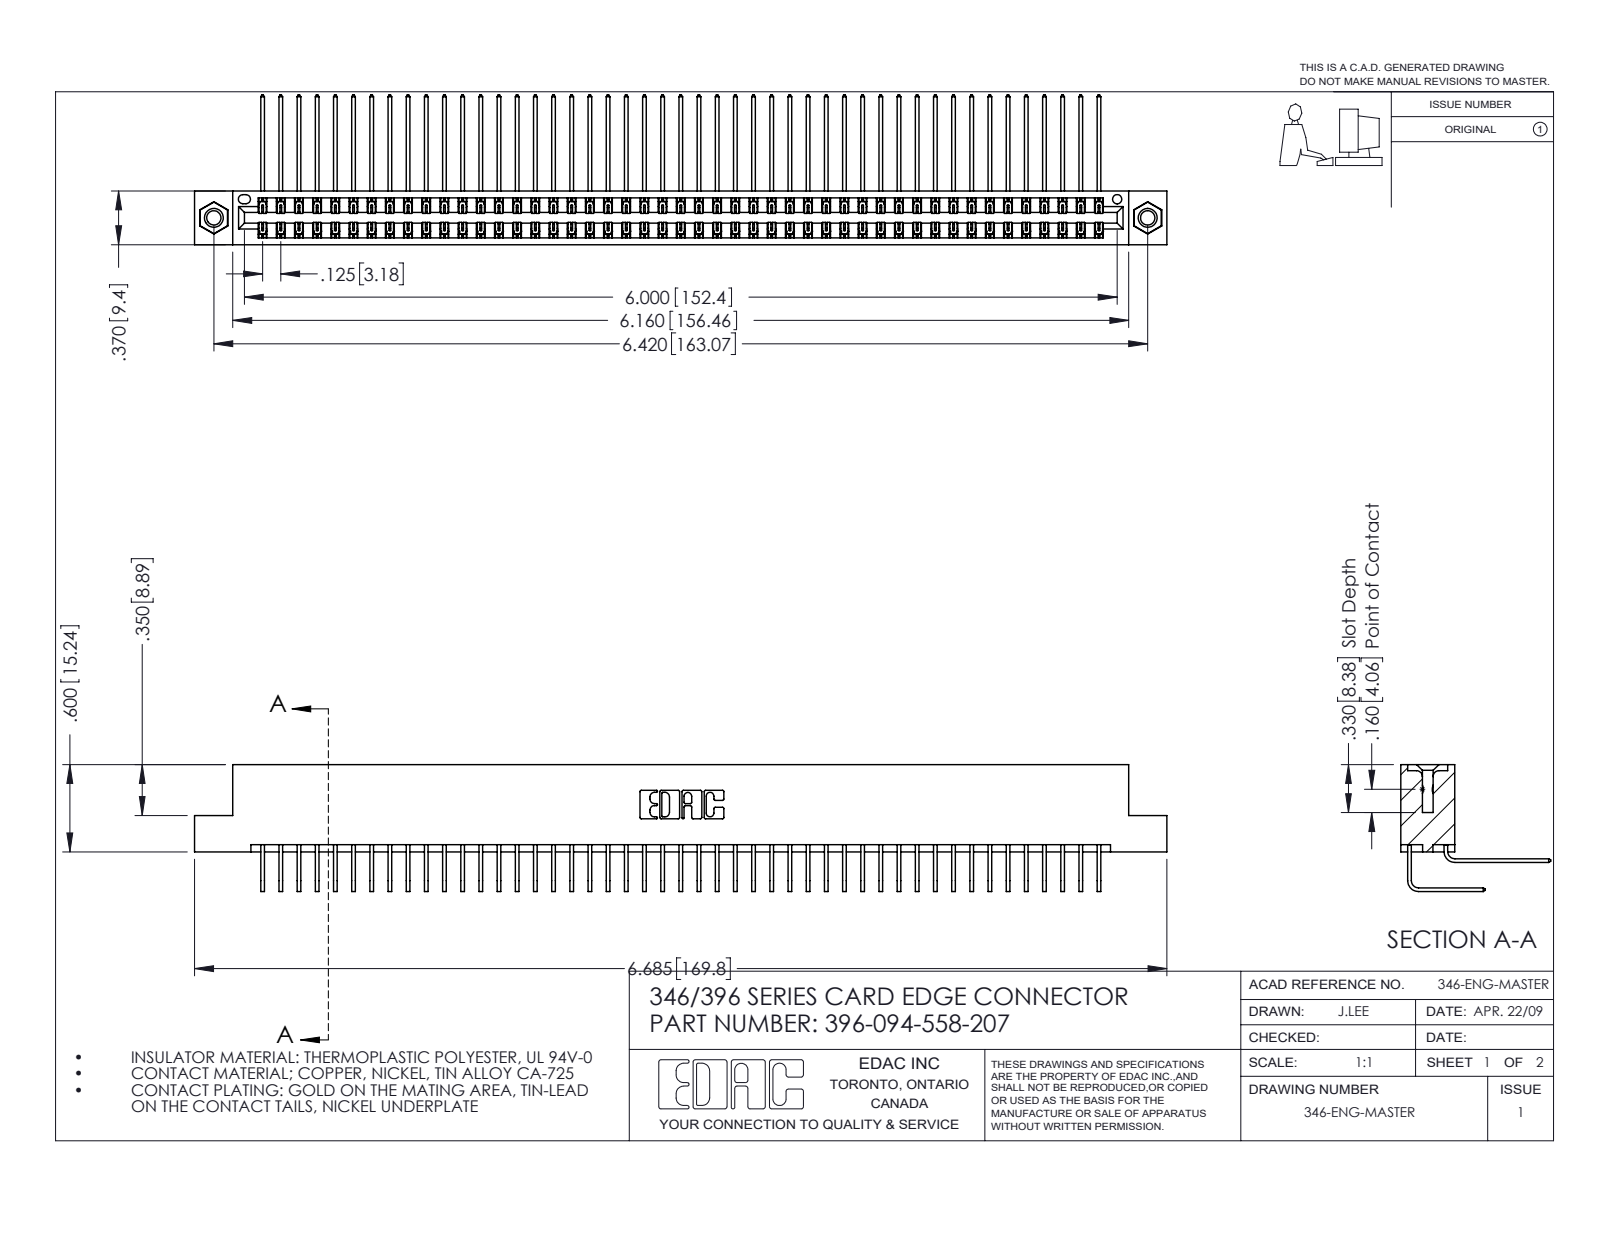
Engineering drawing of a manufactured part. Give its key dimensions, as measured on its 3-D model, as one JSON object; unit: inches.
{"part_name": "345-292-001_558 559 Tail - 1; 396-094-558-207; 345-250-001_345-250-005-103; 345-292-001_558 Tail - 2 (+1 more)", "step_written_by": "SolidWorks 2016 (CONFIG_CONTROL_DESIGN)", "units": "inches", "bodies": {"solids": 97, "faces": 5258, "planar": 3586, "cylindrical": 1656, "other": 16}, "overall_size": [6.685, 1.03, 0.873], "volume_in3": 1.045, "surface_area_in2": 40.69, "round_holes": [[0.098, 2], [0.125, 2], [0.156, 2], [0.064, 1]], "round_bosses_or_shafts": [[0.155, 2]], "partial_cylinders_radius": [[0.006, 141], [0.01, 22], [0.007, 6], [0.031, 6], [0.026, 3], [0.014, 2], [0.022, 2], [0.024, 2]], "face_to_face_distances": [0.048, 0.322, 0.025, 0.37, 0.25, 0.072, 0.298, 0.275, 0.148, 0.222], "hole_center_spacings": [0.246, 6.211, 6.42]}
